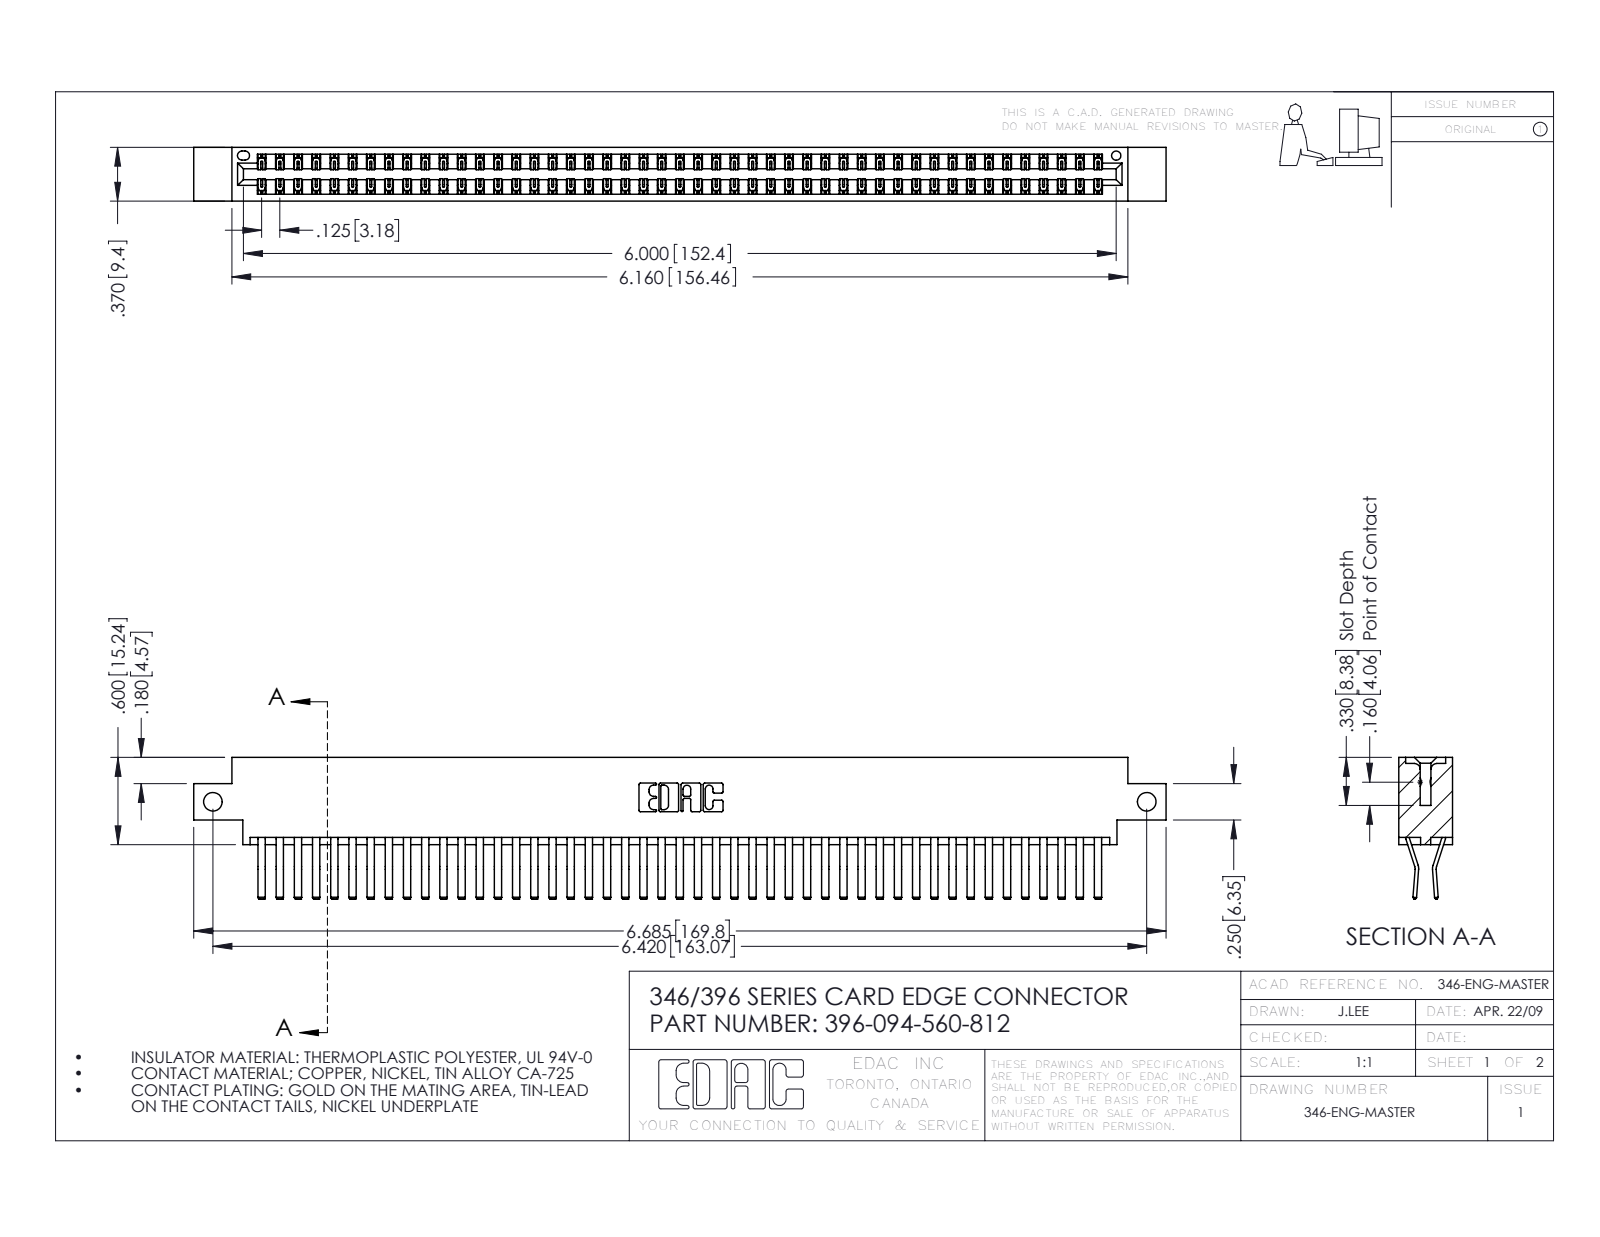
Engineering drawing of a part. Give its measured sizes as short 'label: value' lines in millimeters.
name: 396-094-560-812; 346 Part_0.170 Offset - Side Mount; 345-292-001_560 Tail
written by: SolidWorks 2016 (CONFIG_CONTROL_DESIGN)
unit: mm
bodies: 95 solids, 5202 faces (3370 planar, 1832 cylindrical, 0 other)
size: 169.8 × 24.8 × 9.4
volume: 16 980 mm³; area: 25 090 mm²
holes: 2× ⌀3.3, 1× ⌀1.6
rounds: 141× R0.2, 22× R0.3, 6× R0.2, 6× R0.8, 3× R0.7, 2× R0.3, 2× R0.4, 2× R0.6
face distances: 1.2, 8.2, 9.4, 0.6, 6.4, 1.8, 7.6, 7, 3.8, 5.6
hole spacings: 163.1
